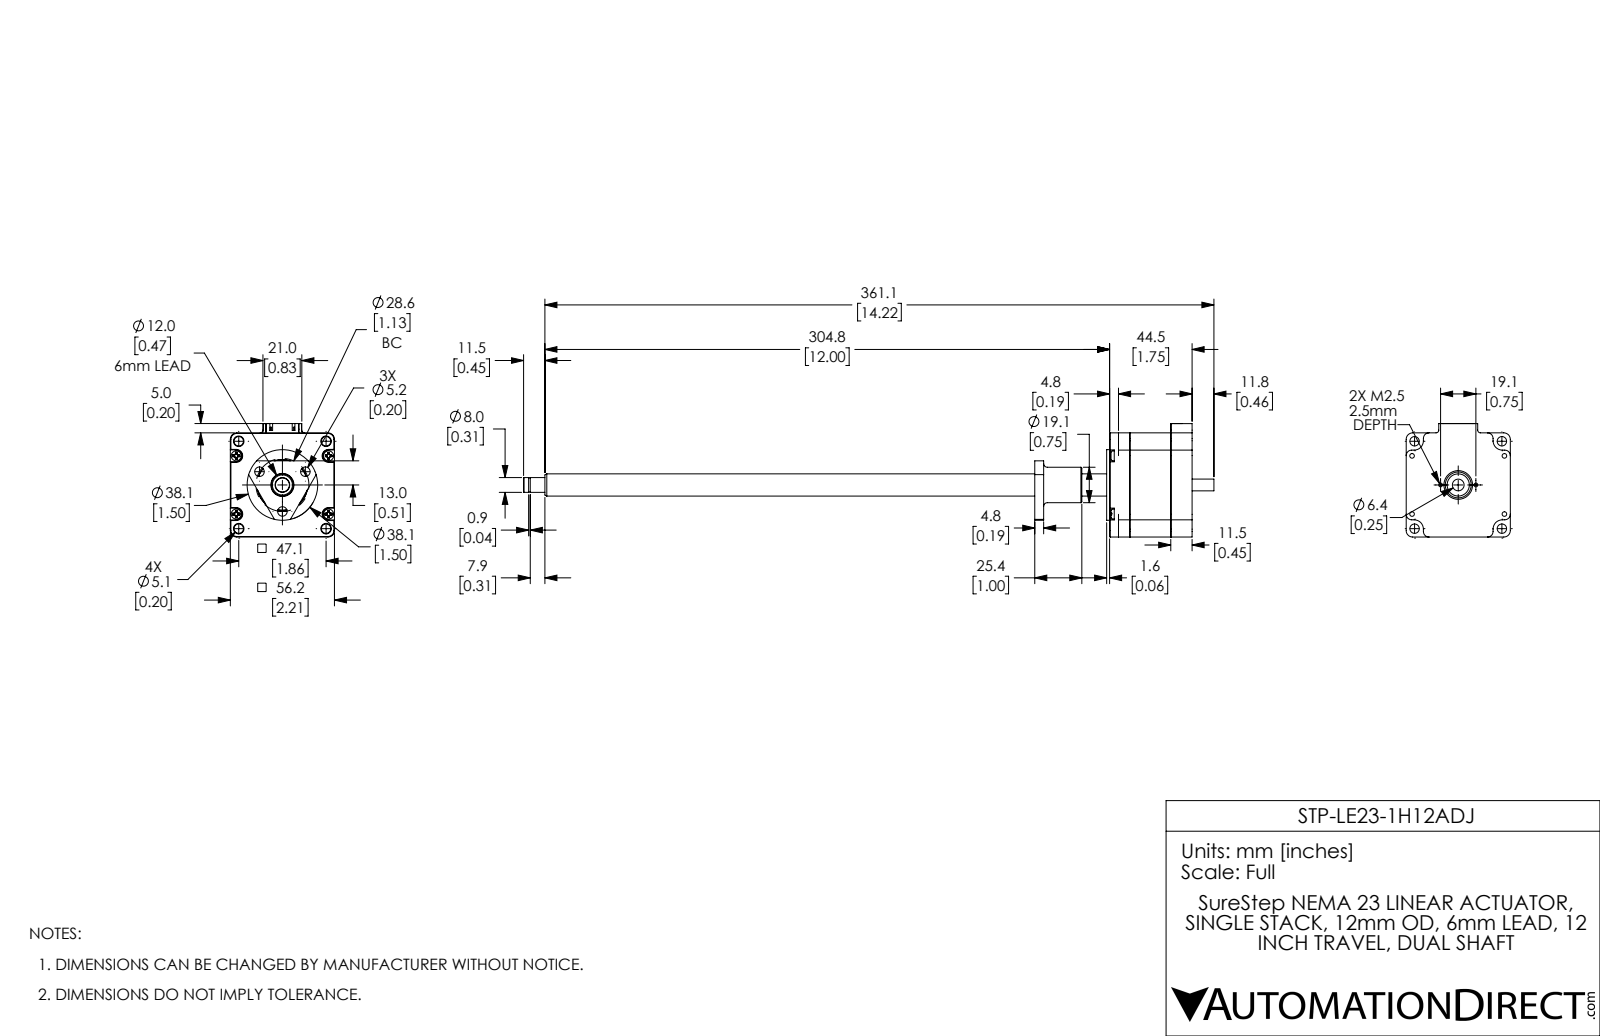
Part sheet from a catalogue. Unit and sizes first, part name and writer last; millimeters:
Units: millimetres
Overall size (bounding box): 372.6 × 61.22 × 56.2
Round holes (diameter × count): ⌀4.5 ×8, ⌀2.5 ×4, ⌀3.3 ×4, ⌀5.1 ×4, ⌀5.16 ×3, ⌀2 ×2, ⌀2.05 ×2, ⌀6.8 ×1, ⌀10.5 ×1, ⌀15.5 ×1, ⌀20 ×1, ⌀24 ×1
Round bosses / shafts (diameter × count): ⌀5.4 ×4, ⌀38.1 ×1, ⌀36 ×1, ⌀35.6 ×1, ⌀34.85 ×1, ⌀19.1 ×1, ⌀16 ×1, ⌀12 ×1
Partial cylindrical surfaces — rounded edges, fillets, slot ends (radius × count): R1.5 ×10, R3 ×8, R1.8 ×4, R3.2 ×4, R3.5 ×4, R5 ×4, R19.3 ×1
Main face-to-face distances: 22, 44.5, 56.2, 11.5, 33.5, 1.6, 51.4, 11, 33, 38.8
Hole centre spacings: 14.12, 24.75, 33.05, 35.01, 45.74, 48.53, 56.99, 6.55
Volume: 142 413 mm³ · Surface area: 56 444 mm²
Bodies: 8 solids, 751 faces (306 planar, 205 cylindrical, 240 other)
Part name (STEP PRODUCT): STP-LE23-1H12ADJ_2; STP-LE23-1H12ADJ_1; STP-LE23-1H12ADJ
STEP written by: SolidWorks 2017 (AUTOMOTIVE_DESIGN)
